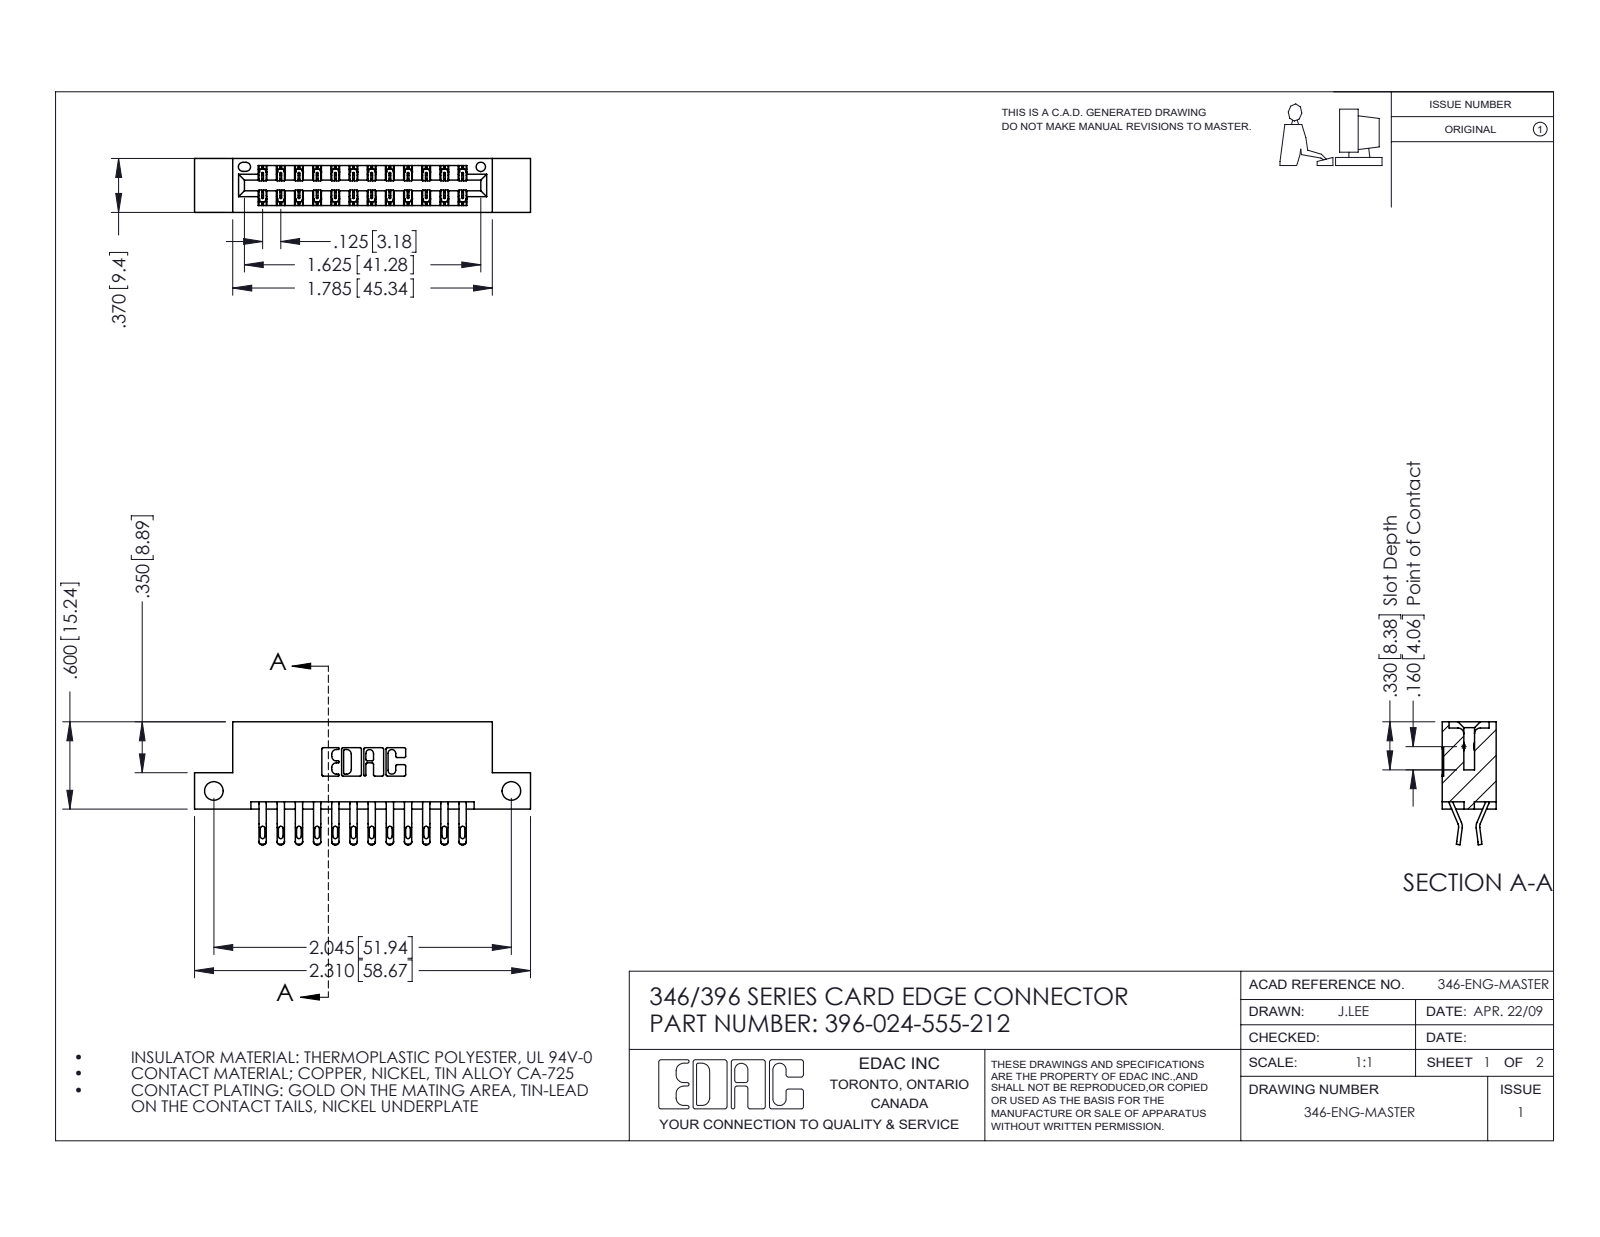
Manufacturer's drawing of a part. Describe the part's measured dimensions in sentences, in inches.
The part is named "396-024-555-212; 346 Part_Flush Mounting Lugs - Side Mount; 345-292-001_555 Tail". Its 3-D file was written by "SolidWorks 2016 (CONFIG_CONTROL_DESIGN)". It is 25 solids with 1514 faces: 868 planar, 646 cylindrical and 0 other. Overall it measures 2.31 by 0.845 by 0.37 inches. Its volume is 0.334 cubic inches and its surface area 11.1 square inches. Round holes: 2 of diameter 0.128, 1 of diameter 0.064. Partial cylindrical surfaces (rounded edges, fillets, slot ends): 48 of radius 0.016, 48 of radius 0.02, 36 of radius 0.006, 22 of radius 0.01, 6 of radius 0.007, 6 of radius 0.031, 3 of radius 0.026, 2 of radius 0.01. The main face-to-face distances are 0.25, 0.048, 0.322, 0.37, 0.025, 0.072, 0.298, 0.275, 0.148, 0.222. The hole center spacings are 2.045.
